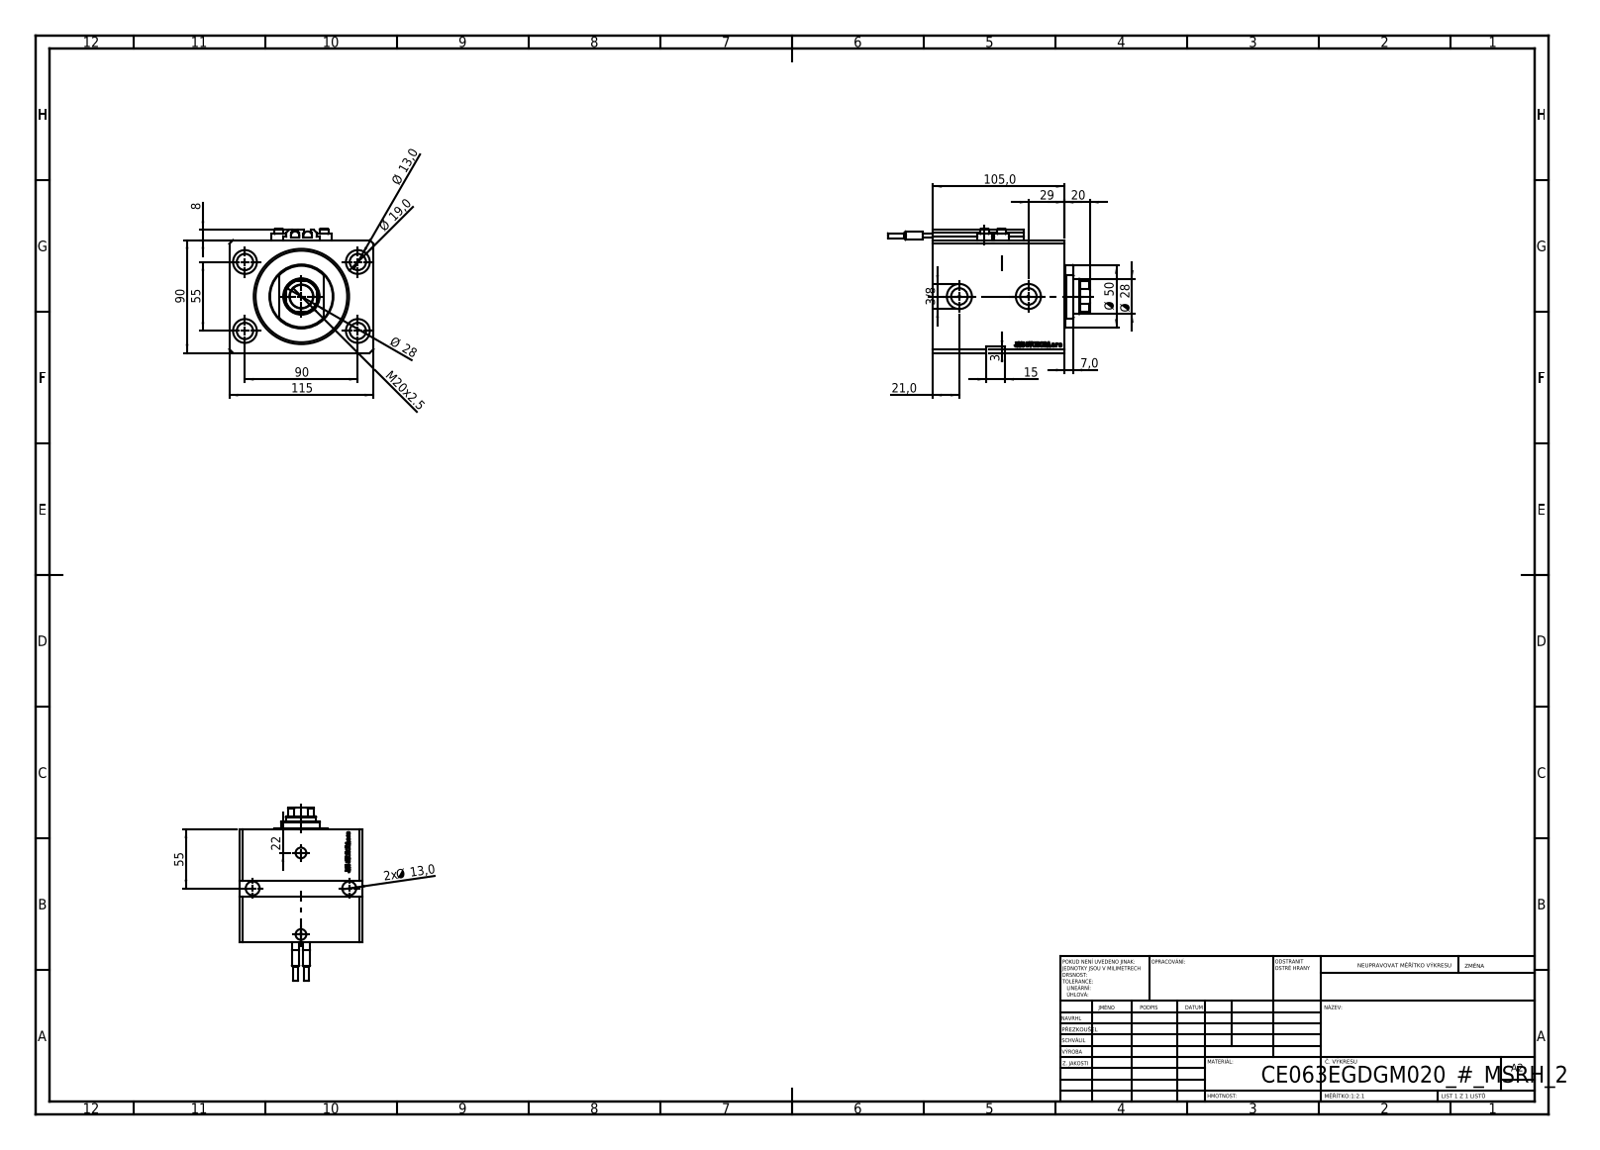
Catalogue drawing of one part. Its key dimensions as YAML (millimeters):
part_name: "V250CE_E_Body; SWITCH_V250CE; ALLEN BOLT V250CE; V250CE_C_VCP (+1 more)"
step_written_by: "SolidWorks 2019 (CONFIG_CONTROL_DESIGN)"
units: millimeters
bodies: {solids: 10, faces: 1175, planar: 579, cylindrical: 150, other: 446}
overall_size: [161, 115, 99]
volume: 954510
surface_area: 157883
round_holes:
  - {diameter: 13, count: 6}
  - {diameter: 1.25, count: 4}
  - {diameter: 4, count: 4}
  - {diameter: 19, count: 4}
  - {diameter: 10, count: 2}
  - {diameter: 13.16, count: 2}
  - {diameter: 20, count: 2}
  - {diameter: 18.5, count: 1}
  - {diameter: 28, count: 1}
  - {diameter: 63, count: 1}
  - {diameter: 76, count: 1}
round_bosses_or_shafts:
  - {diameter: 11.6, count: 4}
  - {diameter: 7, count: 4}
  - {diameter: 6.8, count: 2}
  - {diameter: 6.5, count: 2}
  - {diameter: 4, count: 2}
  - {diameter: 50, count: 1}
partial_cylinders:
  - {radius: 0.2, count: 10}
  - {radius: 13.5, count: 1}
face_to_face_distances: [90, 20, 115, 85, 105, 87.1, 17.9, 67.1, 40, 65]
hole_center_spacings: [52.74, 55, 90, 13.6, 27.39, 28.46, 33.62, 36]
